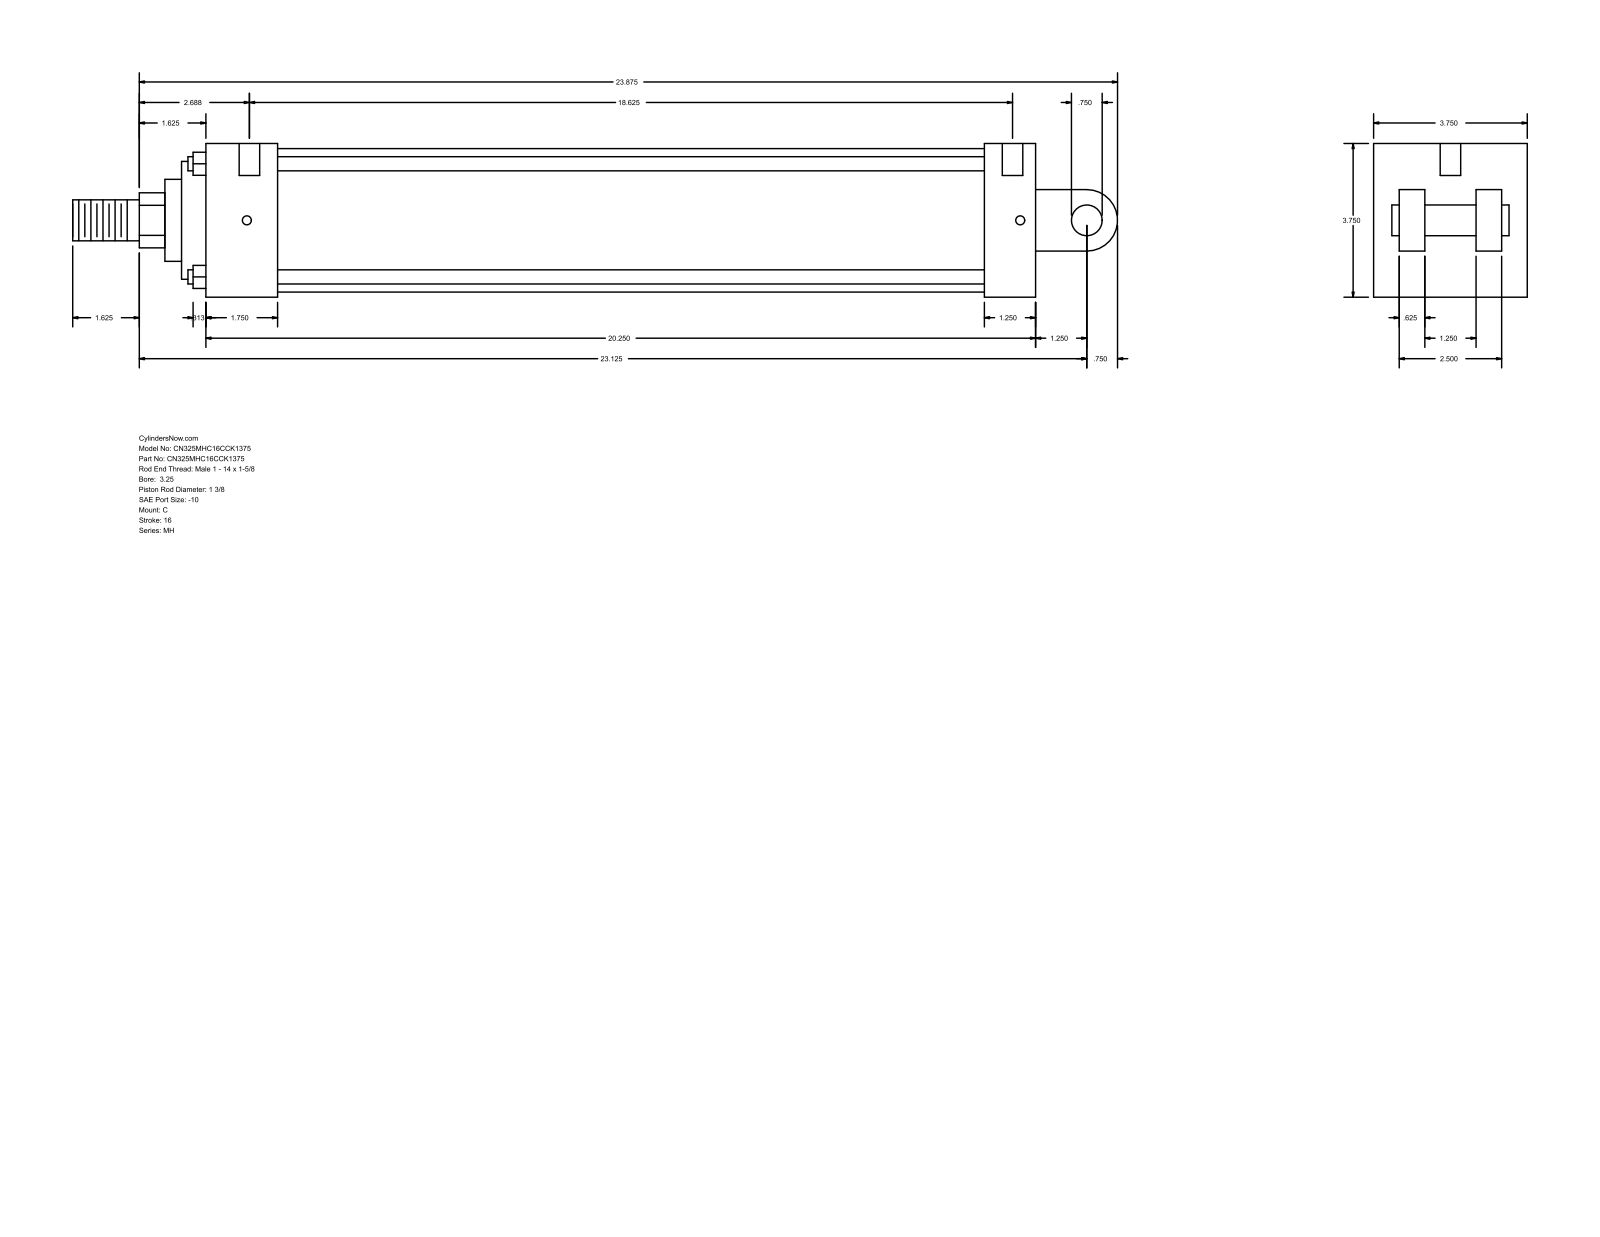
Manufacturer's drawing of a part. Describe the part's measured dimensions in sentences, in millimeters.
The part is named "MH_C__0325_1.375". Its 3-D file was written by "GSSL Pune (CONFIG_CONTROL_DESIGN)". It is 0 solids with 101 faces: 71 planar, 30 cylindrical and 0 other. Overall it measures 647.7 by 95.25 by 95.25 millimeters. Round holes: 4 of diameter 5.56, 2 of diameter 12.7. Round bosses or shafts: 4 of diameter 8.76, 1 of diameter 88.9, 1 of diameter 73.03, 1 of diameter 50.8, 1 of diameter 34.92, 1 of diameter 25.4, 1 of diameter 19.05. Partial cylindrical surfaces (rounded edges, fillets, slot ends): 1 of radius 17.06, 1 of radius 19.05. The main face-to-face distances are 95.24, 15.87, 31.74, 63.5, 514.35, 79.37, 47.63, 44.45, 482.61, 438.16. The hole center spacings are 479.43, 1.59, 4.76, 473.08, 474.67, 477.84.
